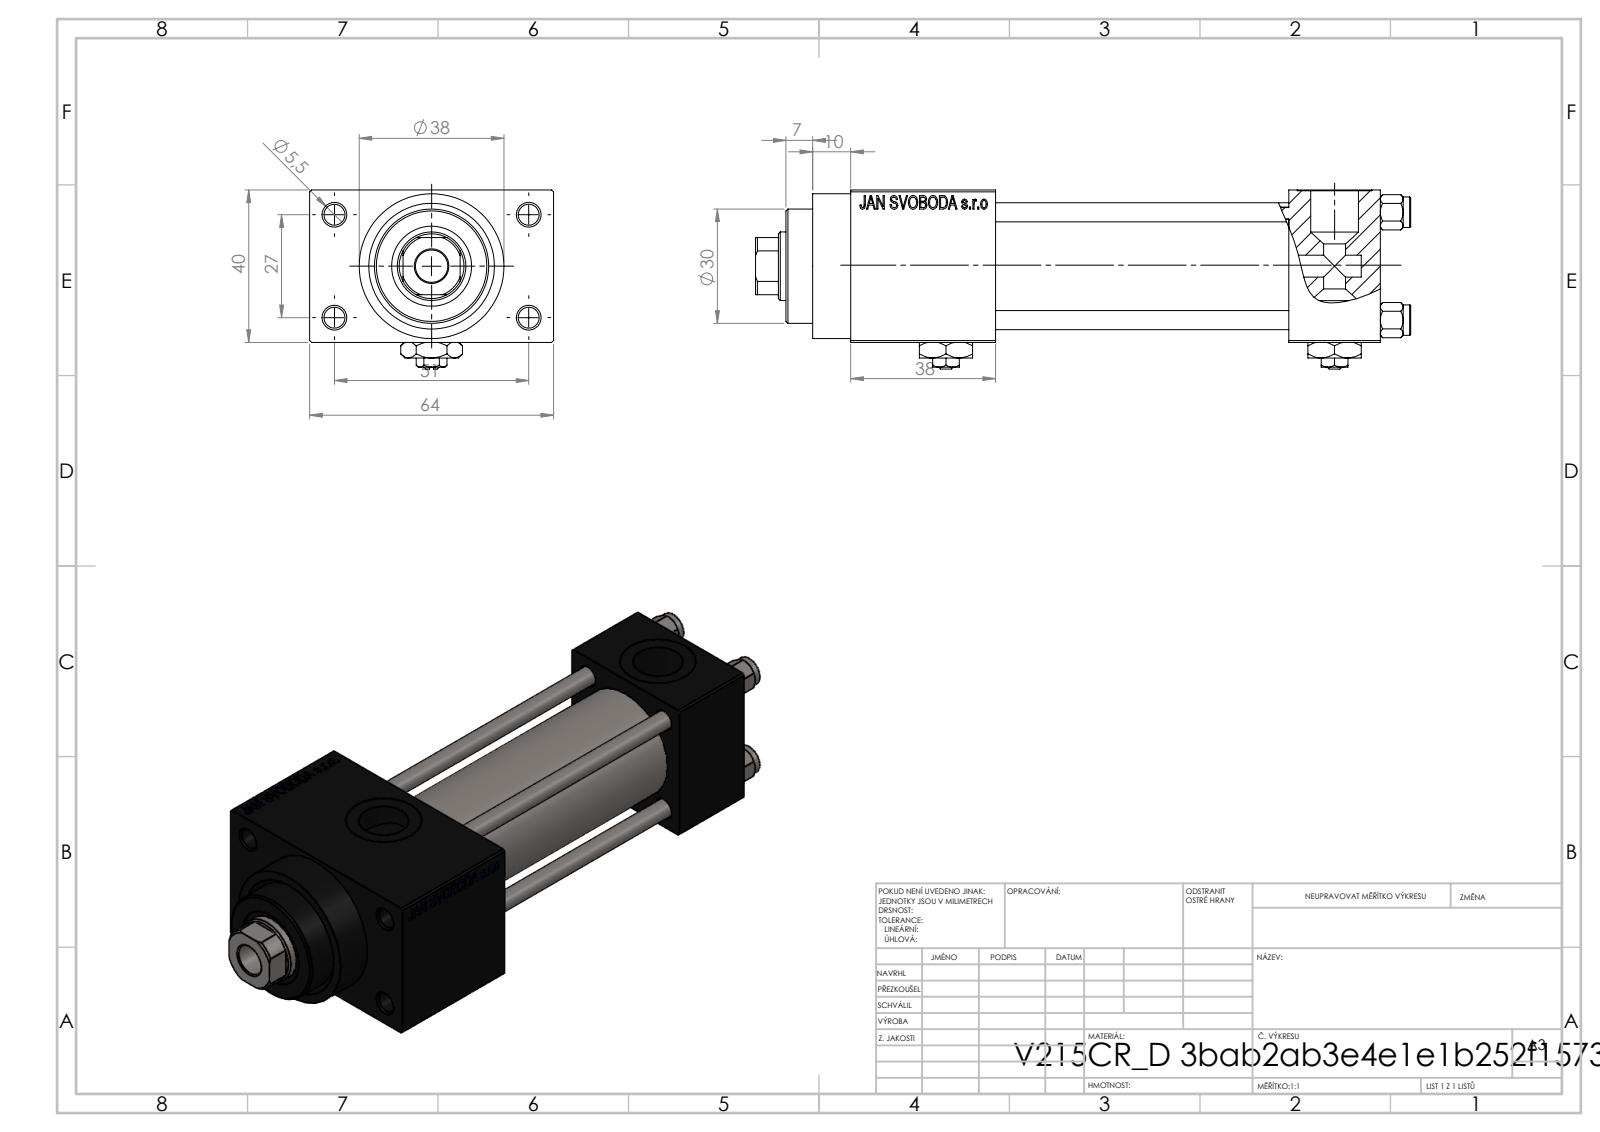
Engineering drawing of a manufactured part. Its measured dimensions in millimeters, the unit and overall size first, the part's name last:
Units: millimetres
Overall size (bounding box): 172 × 64 × 47
Round holes (diameter × count): ⌀5 ×4, ⌀5.5 ×4, ⌀20 ×3, ⌀7 ×2, ⌀13.16 ×2, ⌀8.5 ×1, ⌀18 ×1, ⌀21 ×1, ⌀25 ×1, ⌀30 ×1
Round bosses / shafts (diameter × count): ⌀8 ×4, ⌀38 ×1, ⌀31 ×1
Partial cylindrical surfaces — rounded edges, fillets, slot ends (radius × count): R8.5 ×1
Main face-to-face distances: 40, 12, 52, 77, 24, 101, 64, 38, 115, 139
Hole centre spacings: 11.37, 20.01, 28.3, 28.85, 29.89, 39.66, 48.34, 27
Volume: 197 560 mm³ · Surface area: 74 644 mm²
Bodies: 13 solids, 1201 faces (541 planar, 98 cylindrical, 562 other)
Part name (STEP PRODUCT): NUT_M5_D; Zatka_pro_OIL_PORT; V215CR_D_TYCINKA; V215CR_VCP_D (+2 more)
STEP written by: SolidWorks 2019 (CONFIG_CONTROL_DESIGN)
